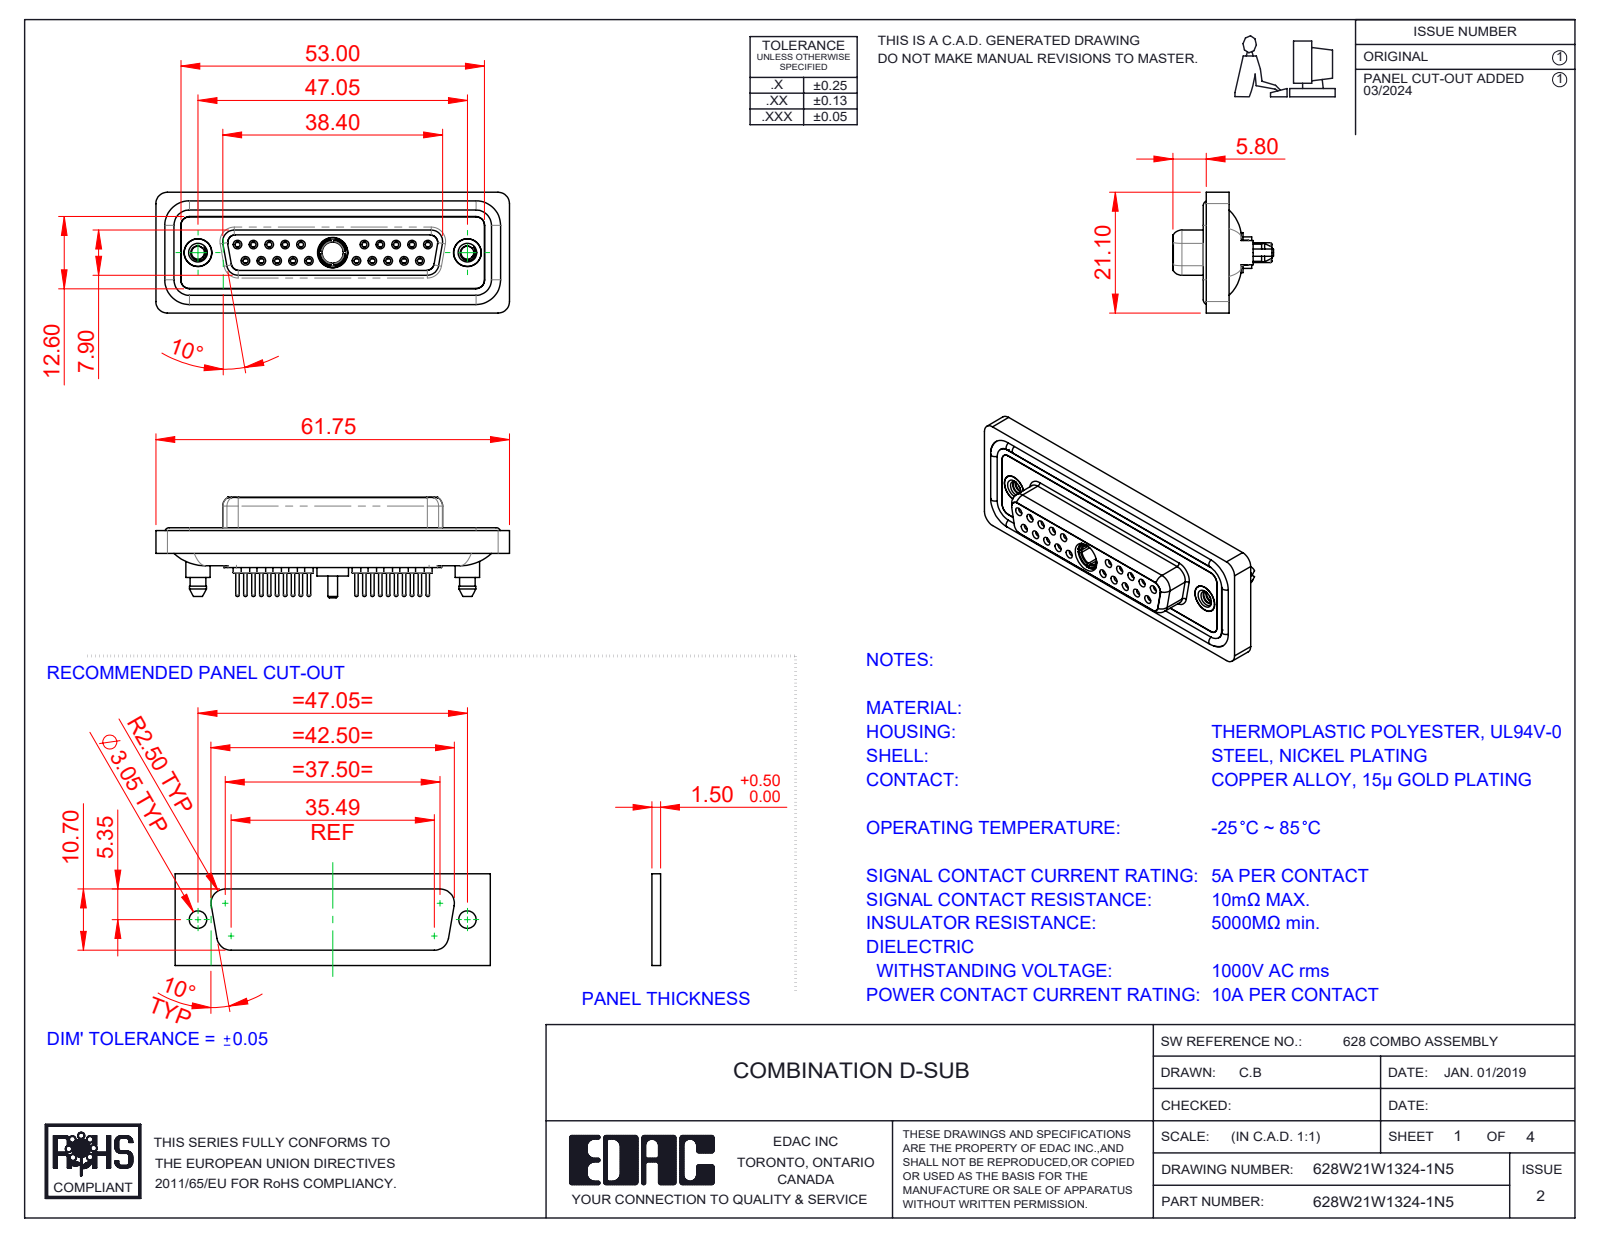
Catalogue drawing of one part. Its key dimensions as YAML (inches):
part_name: "628Combo Waterproof Housing_25 Contacts; Power Socket_10A S; 628Combo Shell Front_25 Contacts; 628Combo Housing_21W1 (+5 more)"
step_written_by: "SolidWorks 2023 (CONFIG_CONTROL_DESIGN)"
units: inches
bodies: {solids: 29, faces: 1610, planar: 450, cylindrical: 623, other: 537}
overall_size: [2.431, 0.831, 0.691]
volume: 0.518
surface_area: 22.2
round_holes:
  - {diameter: 0.035, count: 20}
  - {diameter: 0.043, count: 20}
  - {diameter: 0.059, count: 20}
  - {diameter: 0.079, count: 20}
  - {diameter: 0.063, count: 10}
  - {diameter: 0.067, count: 10}
  - {diameter: 0.191, count: 3}
  - {diameter: 0.089, count: 2}
  - {diameter: 0.157, count: 2}
  - {diameter: 0.159, count: 2}
  - {diameter: 0.197, count: 2}
  - {diameter: 0.146, count: 1}
round_bosses_or_shafts:
  - {diameter: 0.087, count: 20}
  - {diameter: 0.024, count: 20}
  - {diameter: 0.063, count: 14}
  - {diameter: 0.213, count: 2}
  - {diameter: 0.195, count: 2}
  - {diameter: 0.189, count: 2}
  - {diameter: 0.167, count: 2}
  - {diameter: 0.217, count: 1}
partial_cylinders:
  - {radius: 0.059, count: 24}
  - {radius: 0.079, count: 18}
  - {radius: 0.063, count: 10}
  - {radius: 0.053, count: 8}
  - {radius: 0.01, count: 4}
  - {radius: 0.02, count: 4}
  - {radius: 0.024, count: 4}
  - {radius: 0.026, count: 4}
face_to_face_distances: [0.016, 0.071, 0.293, 0.26, 0.222, 0.063, 0.02, 0.278, 0.114, 0.043]
hole_center_spacings: [0.124, 0.109, 0.218, 0.198, 0.327, 0.294, 0.654, 0.763]
